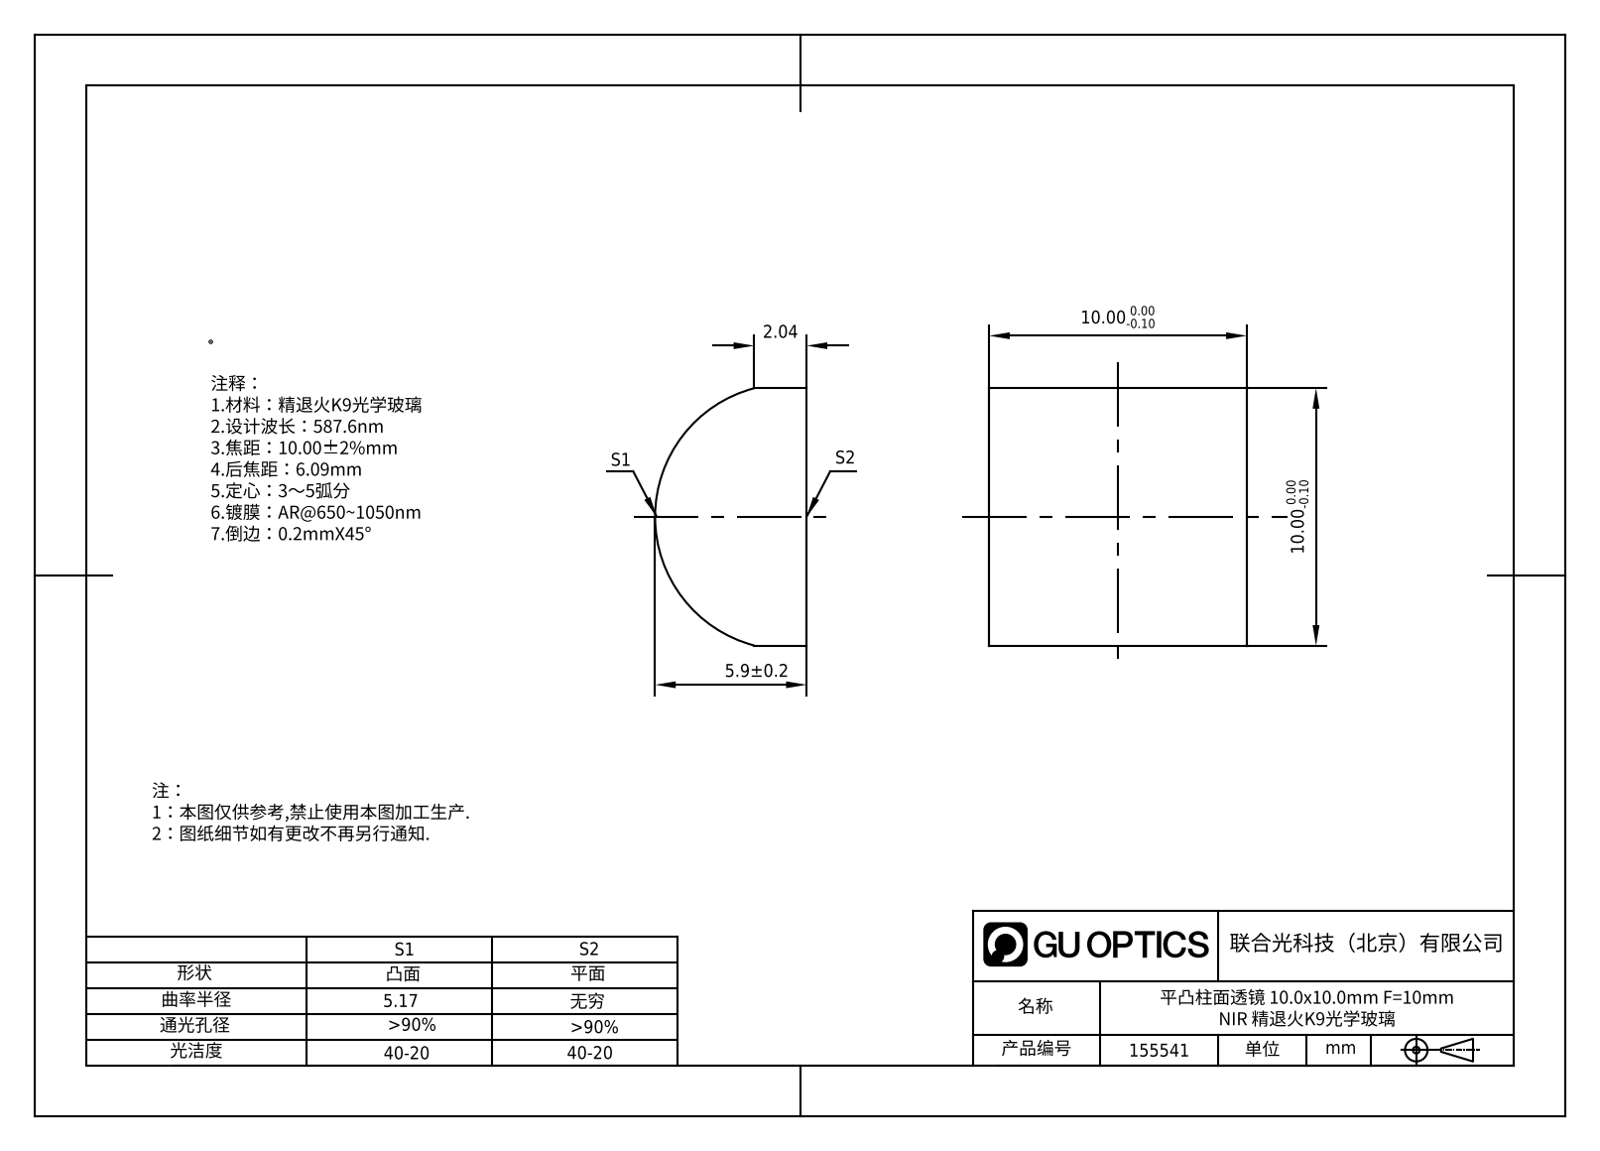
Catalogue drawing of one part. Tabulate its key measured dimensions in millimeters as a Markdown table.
| quantity | value |
| --- | --- |
| part name | 1555517 |
| STEP written by | SolidWorks 2020 (CONFIG_CONTROL_DESIGN) |
| units | millimeters |
| bodies | 1 solid, 7 faces (5 planar, 2 cylindrical, 0 other) |
| overall size | 10 × 10 × 5.89 |
| volume | 489 mm³ |
| surface area | 375 mm² |
| partial cylindrical surfaces (radius × count) | 5.17 × 1 |
| main face-to-face distances | 10 |
